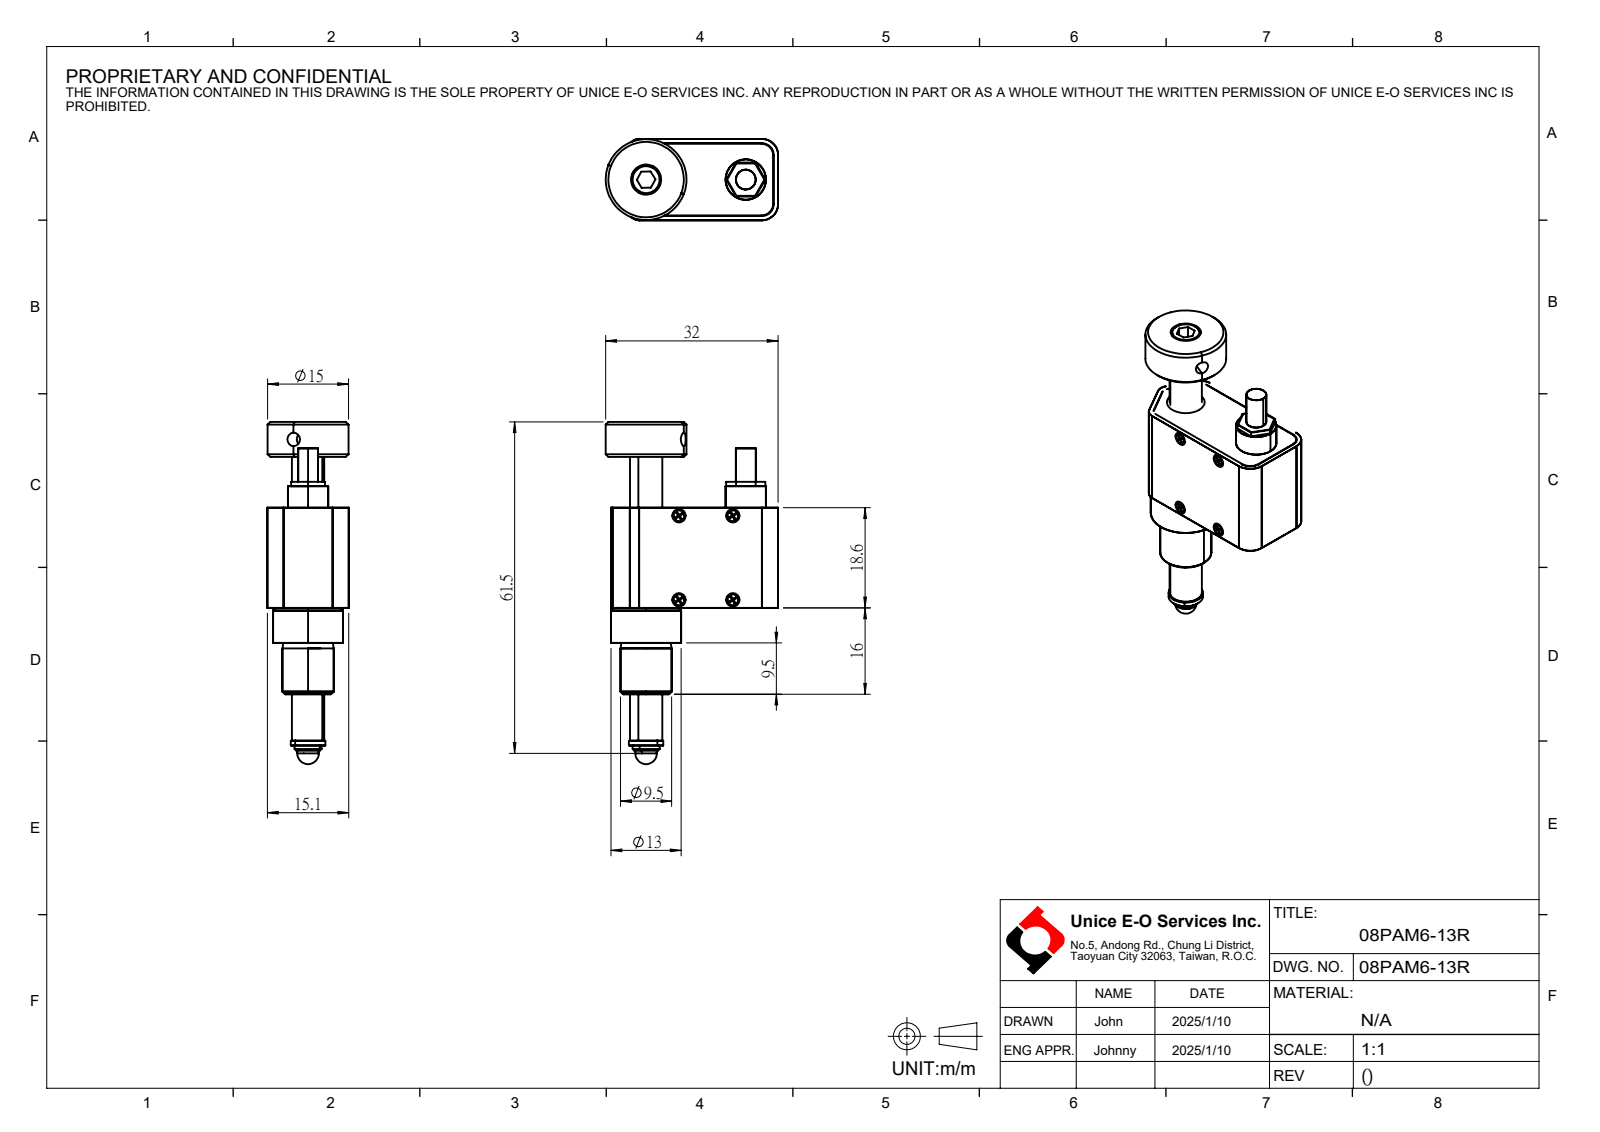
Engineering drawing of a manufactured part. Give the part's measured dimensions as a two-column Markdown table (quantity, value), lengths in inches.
| quantity | value |
| --- | --- |
| part name | 08PAM6-13R |
| STEP written by | SolidWorks 2024 (CONFIG_CONTROL_DESIGN) |
| units | inches |
| bodies | 0 solids, 261 faces (141 planar, 67 cylindrical, 53 other) |
| overall size | 2.5 × 1.243 × 0.975 |
| round holes (diameter × count) | 0.055 × 2, 0.079 × 2, 0.098 × 1, 0.157 × 1, 0.197 × 1, 0.22 × 1, 0.295 × 1, 0.358 × 1, 0.374 × 1, 0.512 × 1 |
| round bosses / shafts (diameter × count) | 0.079 × 2, 0.055 × 2, 0.591 × 1, 0.252 × 1, 0.236 × 1, 0.146 × 1 |
| partial cylindrical surfaces (radius × count) | 0.079 × 3, 0.118 × 2 |
| main face-to-face distances | 0.031, 0.563, 0.732, 0.531, 0.594, 1.359, 0.256, 0.627, 1.103, 0.371 |
| hole center spacings | 0.728, 0.73 |
